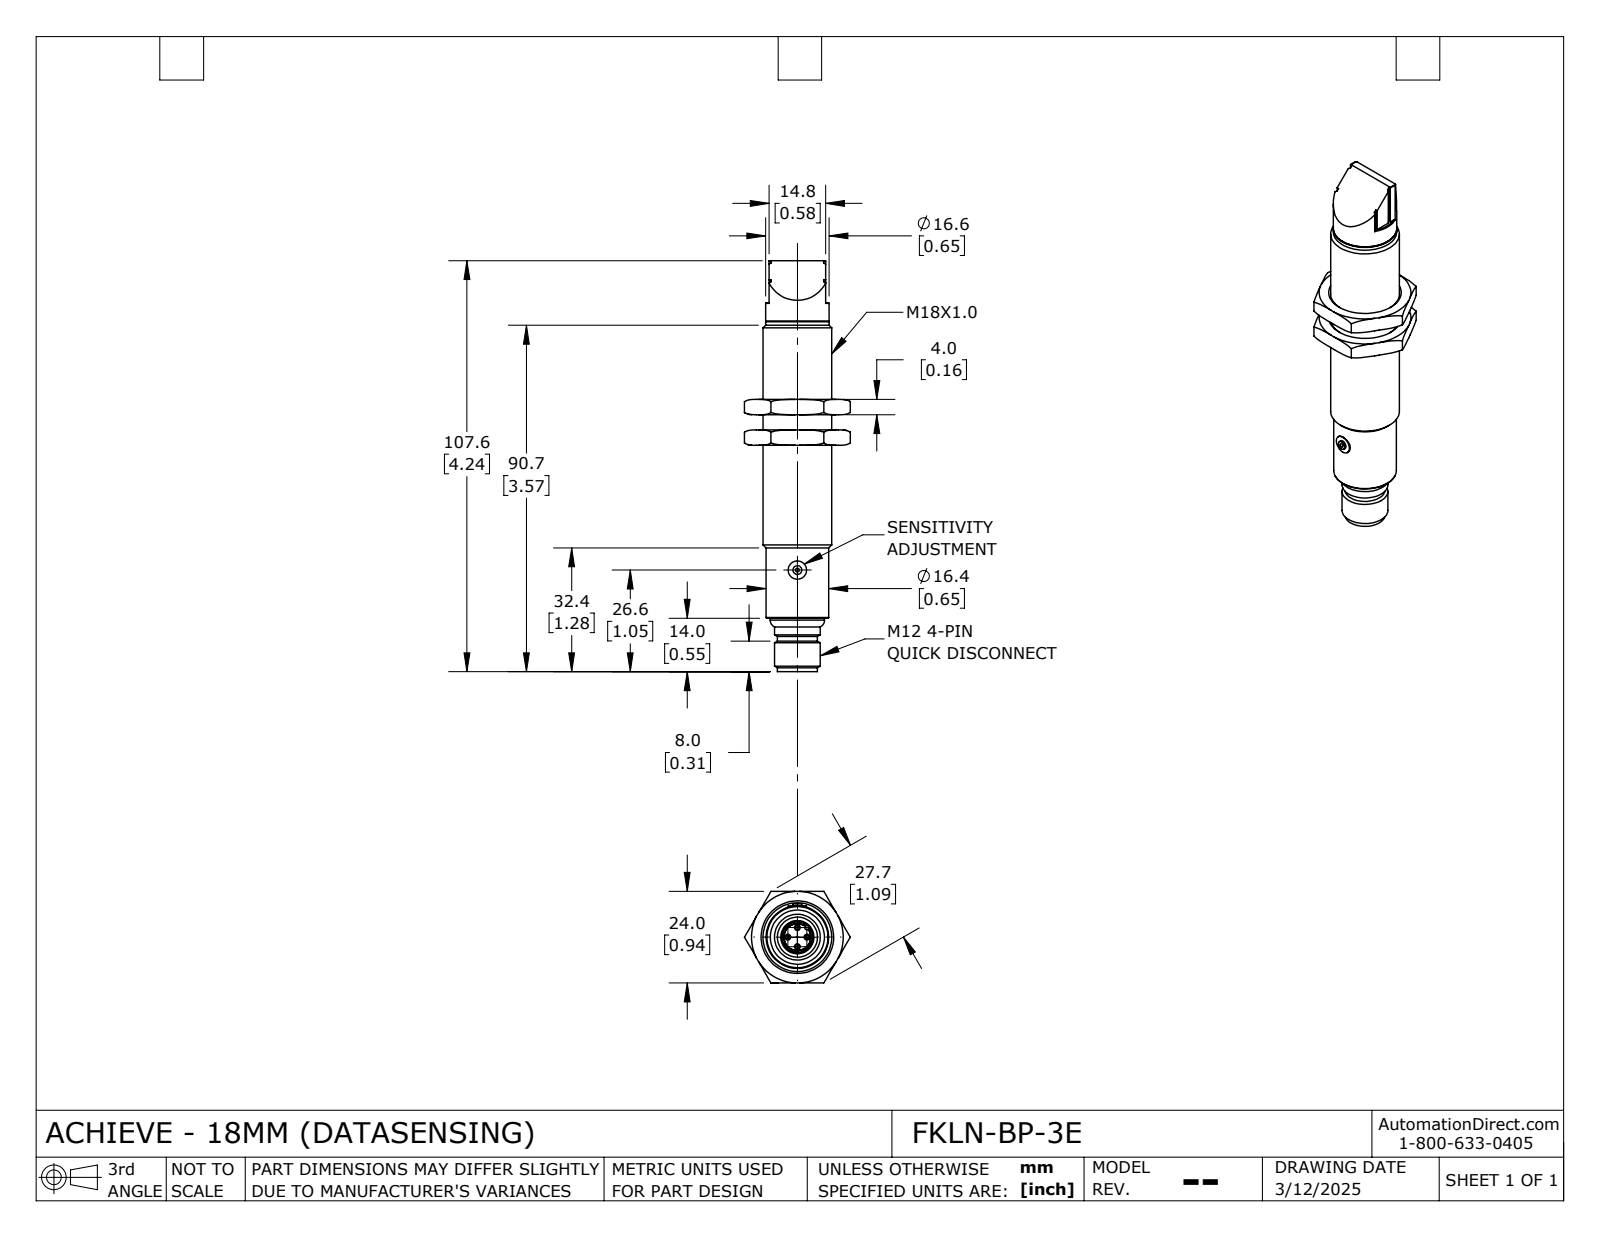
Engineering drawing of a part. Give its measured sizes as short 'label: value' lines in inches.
name: FKLN-BP-3E_Default
written by: SolidWorks 2024 (CONFIG_CONTROL_DESIGN)
unit: in
bodies: 3 solids, 146 faces (64 planar, 30 cylindrical, 52 other)
size: 4.236 × 1.091 × 0.945
volume: 1.472 in³; area: 14.05 in²
holes: 1× ⌀0.185, 1× ⌀0.278, 1× ⌀0.327, 1× ⌀0.583, 1× ⌀0.709
bosses: 4× ⌀0.039, 1× ⌀0.654, 1× ⌀0.646, 1× ⌀0.559, 1× ⌀0.472, 1× ⌀0.413, 1× ⌀0.276, 1× ⌀0.189
rounds: 2× R0.004, 2× R0.02, 1× R0.024, 1× R0.297
face distances: 0.157, 0.315, 0.945, 1.253, 1.261, 0.938, 0.946, 0.472, 1.41, 1.418
